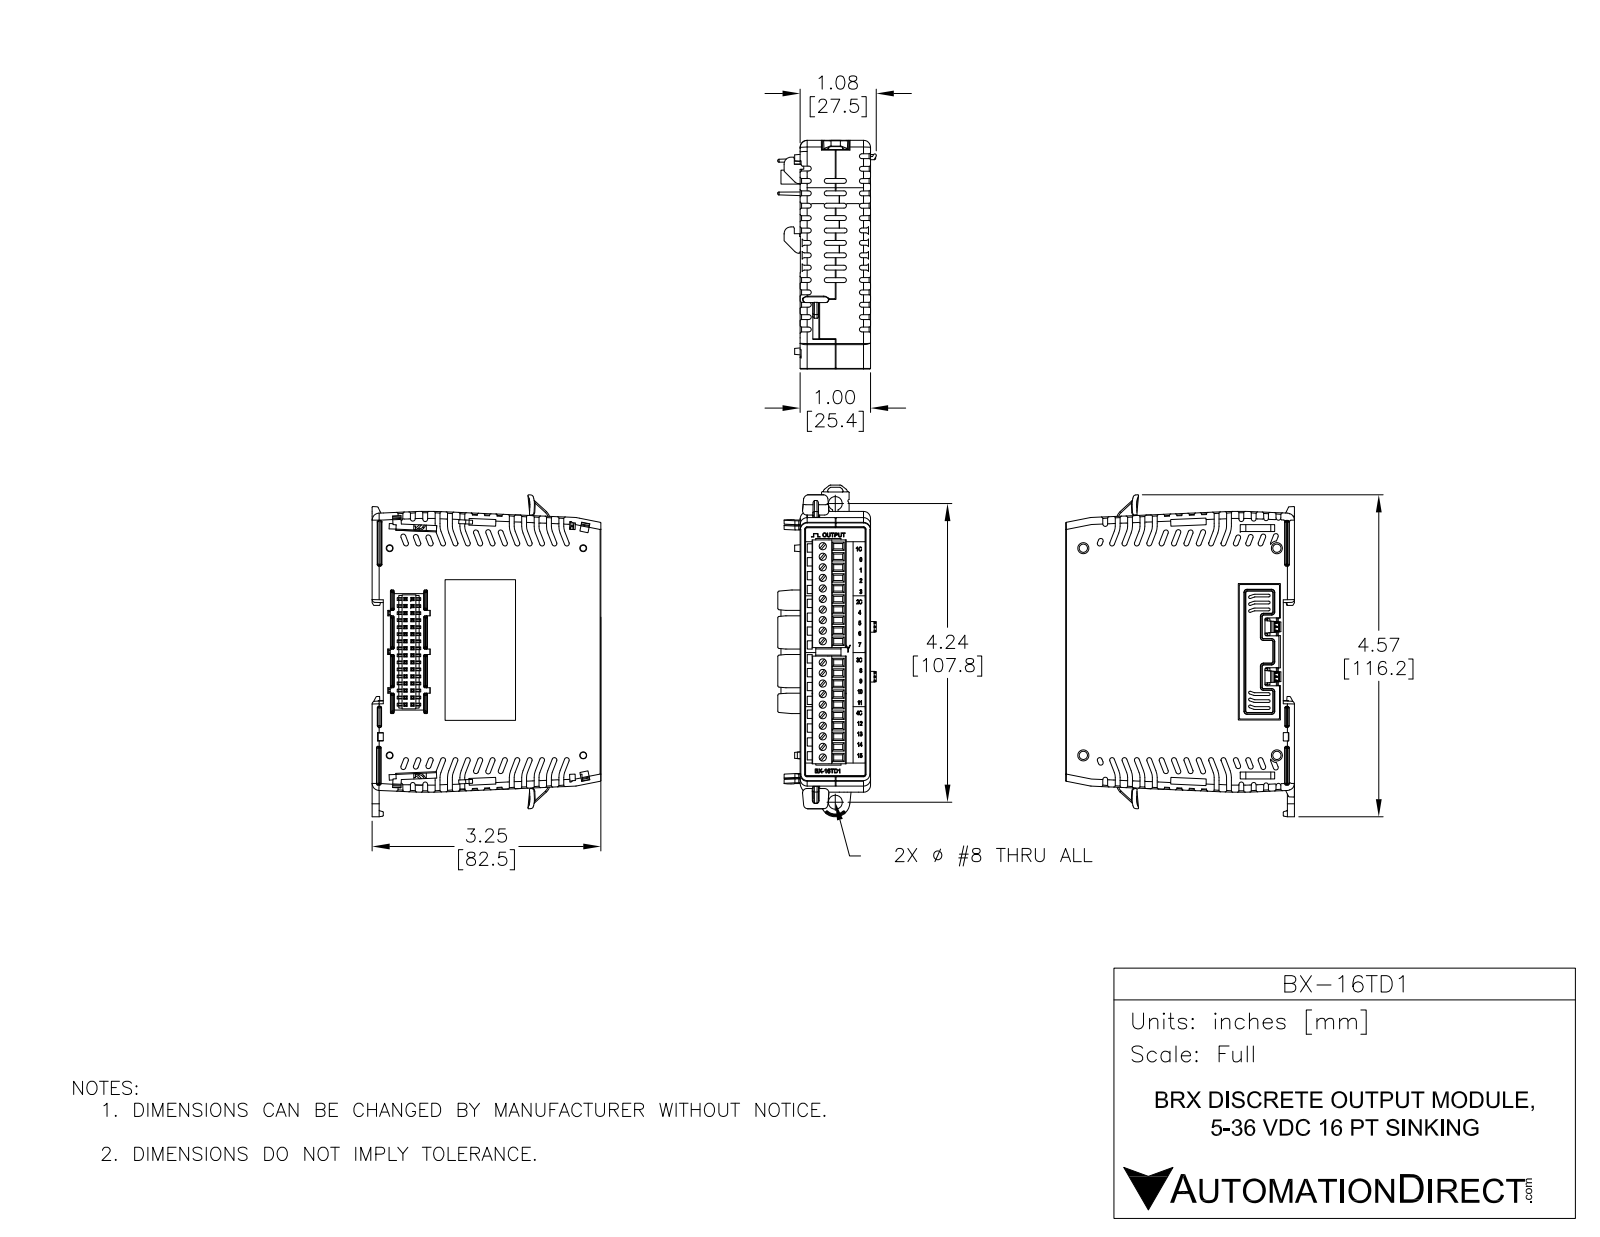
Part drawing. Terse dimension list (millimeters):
name: BX-16TD1
written by: SolidWorks 2017 (AUTOMOTIVE_DESIGN)
unit: mm
bodies: 12 solids, 4168 faces (2929 planar, 663 cylindrical, 576 other)
size: 116.5 × 82.6 × 35.6
volume: 189 800 mm³; area: 46 780 mm²
holes: 2× ⌀1.2, 2× ⌀1.7, 2× ⌀3, 2× ⌀3, 1× ⌀5.1
bosses: 2× ⌀1.6, 2× ⌀1.5
rounds: 102× R0.1, 101× R0.2, 47× R0.3, 34× R0.5, 24× R0.1, 20× R1.6, 14× R3, 13× R1
face distances: 25.4, 81.6, 81.8, 12.1, 1, 4, 77.5, 77.8, 2.5, 20
hole spacings: 2.5, 20.9, 23.3, 33, 53.2, 55.7, 65.7, 66.5
